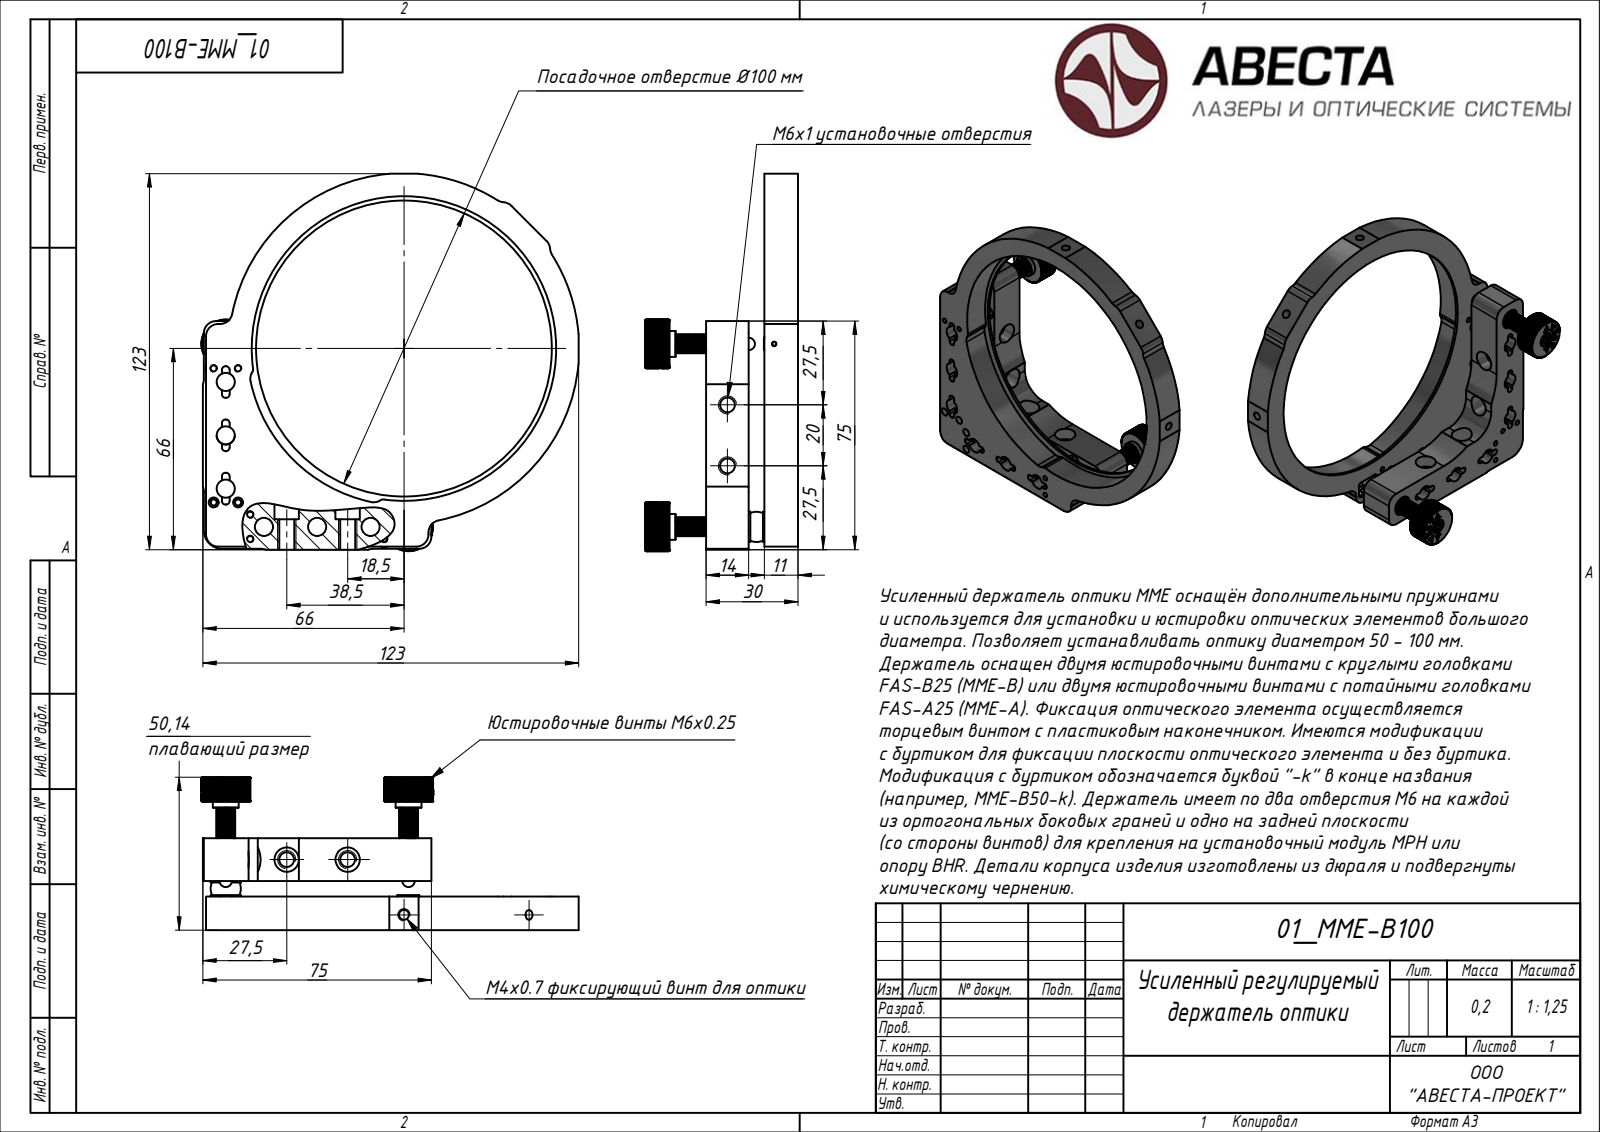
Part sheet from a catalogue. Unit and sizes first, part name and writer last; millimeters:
Units: millimetres
Overall size (bounding box): 266.65 × 182.91 × 124.54
Main face-to-face distances: 11, 0.97, 67.75, 0.82, 68.72, 0.98, 67.74, 66.77, 30.14, 19.14
Volume: 371 677 mm³ · Surface area: 200 497 mm²
Bodies: 98 solids, 3922 faces (1680 planar, 0 cylindrical, 2242 other)
STEP written by: ST-DEVELOPER v15 (AUTOMOTIVE_DESIGN)
